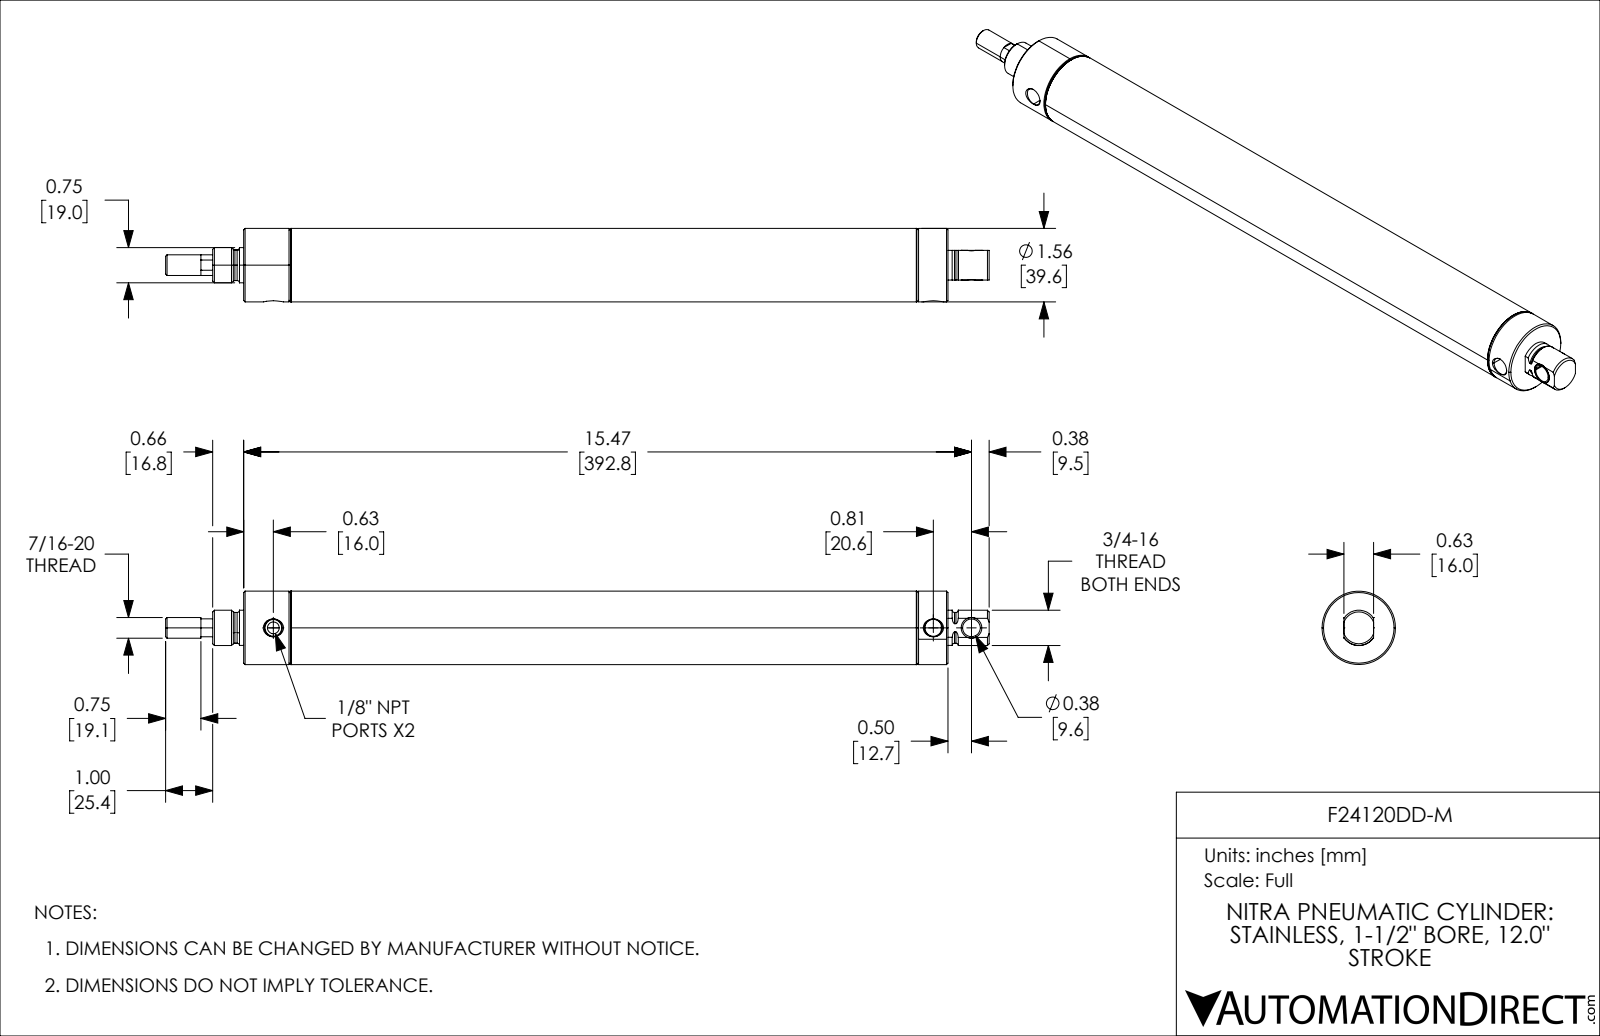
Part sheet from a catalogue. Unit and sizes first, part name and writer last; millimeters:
Units: millimetres
Overall size (bounding box): 444.5 × 39.62 × 39.62
Round holes (diameter × count): ⌀6.35 ×1, ⌀9.14 ×1, ⌀9.55 ×1, ⌀11.15 ×1, ⌀11.73 ×1, ⌀13.51 ×1, ⌀26.97 ×1, ⌀36.36 ×1
Round bosses / shafts (diameter × count): ⌀39.62 ×1, ⌀38.39 ×1, ⌀19.05 ×1, ⌀18.99 ×1, ⌀16.61 ×1, ⌀16.6 ×1, ⌀11.13 ×1, ⌀11.11 ×1
Main face-to-face distances: 22.22, 44.45, 304.8, 327.02, 349.25, 22.23, 30.86, 335.66, 357.88, 380.11
Hole centre spacings: 20.57, 356.24, 376.81
Volume: 148 249 mm³ · Surface area: 120 970 mm²
Bodies: 5 solids, 157 faces (35 planar, 58 cylindrical, 64 other)
Part name (STEP PRODUCT): F24120DD-M; F24120DD-M_5; F24120DD-M_7; F24120DD-M_9 (+2 more)
STEP written by: SolidWorks 2021 (CONFIG_CONTROL_DESIGN)
